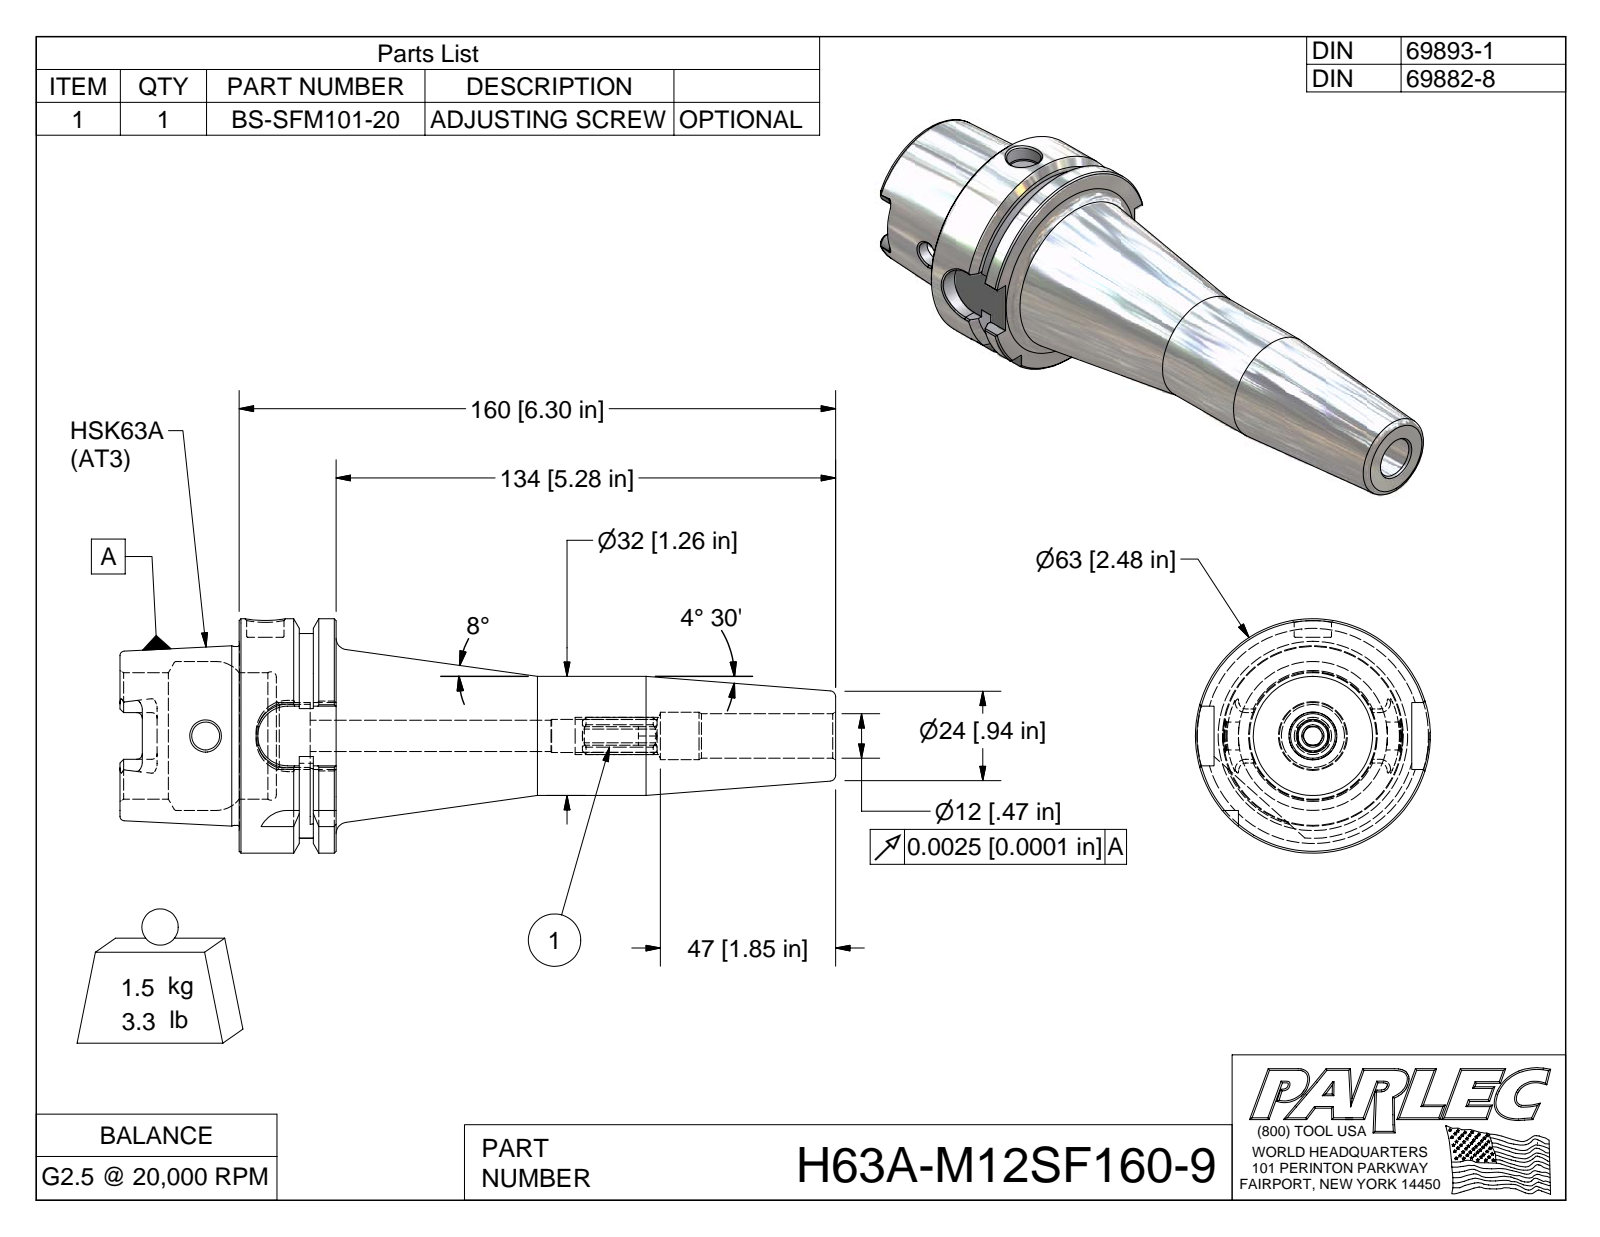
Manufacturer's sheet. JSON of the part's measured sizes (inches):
{"part_name": "H63A-M12SF160-9; H63A-M12SF160-9-1; BS-SFM101-20", "step_written_by": "Autodesk Inventor 2009 (AUTOMOTIVE_DESIGN)", "units": "inches", "bodies": {"solids": 2, "faces": 160, "planar": 59, "cylindrical": 35, "other": 66}, "overall_size": [7.559, 2.48, 2.48], "volume_in3": 11.88, "surface_area_in2": 62.23, "round_holes": [[0.295, 1], [0.394, 1], [0.471, 1], [0.501, 1], [0.666, 1], [1.339, 1], [1.575, 1]], "round_bosses_or_shafts": [[2.48, 1], [1.891, 1], [1.26, 1]], "partial_cylinders_radius": [[0.059, 6], [0.113, 4], [0.315, 4], [0.197, 1], [1.083, 1]], "face_to_face_distances": [1.024, 0.241, 0.389, 0.63, 0.394, 1.26, 1.654, 2.283, 1.894, 0.635]}
